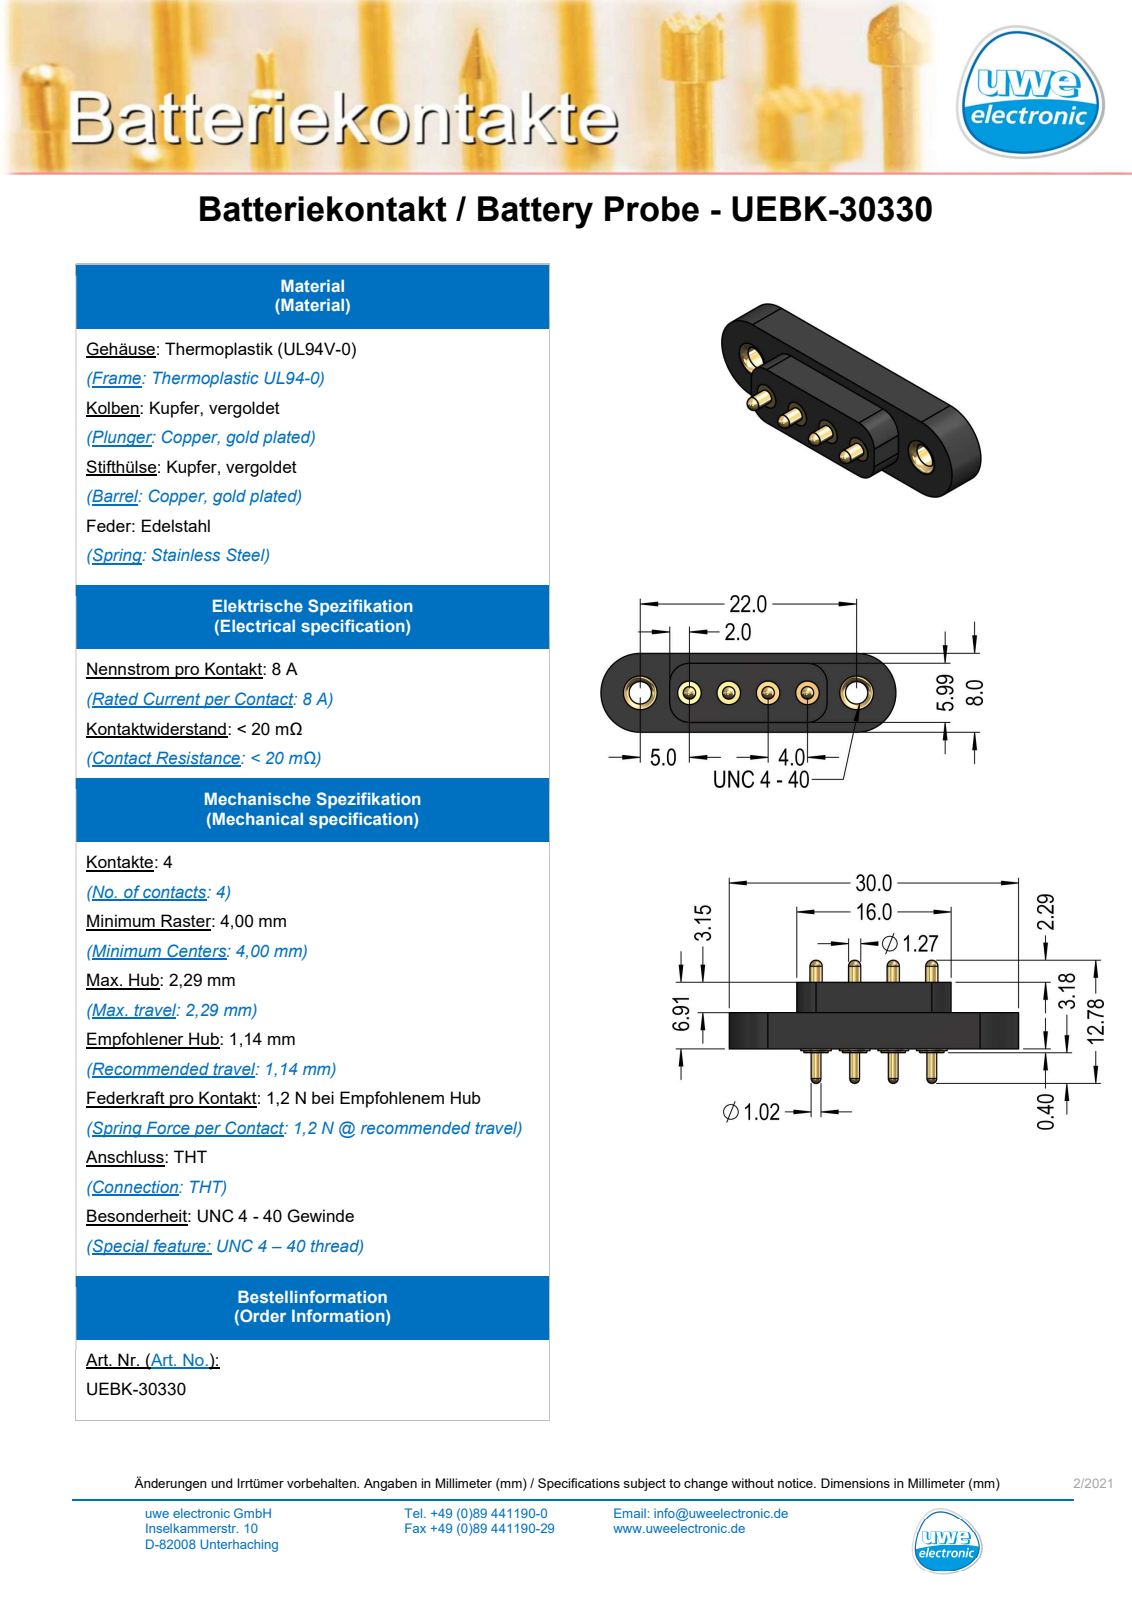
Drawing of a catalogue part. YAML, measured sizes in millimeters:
part_name: "UEBK-30330-Gehäuse; UEBK-30330-Pin; UEBK-30330"
step_written_by: "SolidWorks 2020 (AUTOMOTIVE_DESIGN)"
units: millimeters
bodies: {solids: 5, faces: 172, planar: 33, cylindrical: 91, other: 48}
overall_size: [30, 12.78, 8]
volume: 1151
surface_area: 1409
round_holes:
  - {diameter: 2.27, count: 2}
round_bosses_or_shafts:
  - {diameter: 3.18, count: 4}
  - {diameter: 2.54, count: 4}
  - {diameter: 2.51, count: 4}
  - {diameter: 2.39, count: 4}
  - {diameter: 1.27, count: 4}
  - {diameter: 1.02, count: 4}
partial_cylinders:
  - {radius: 2, count: 4}
  - {radius: 4, count: 2}
face_to_face_distances: [3.76, 6.9, 3.14, 8, 1.01, 7, 5.99, 6.99, 1, 0.41]
hole_center_spacings: [22]
